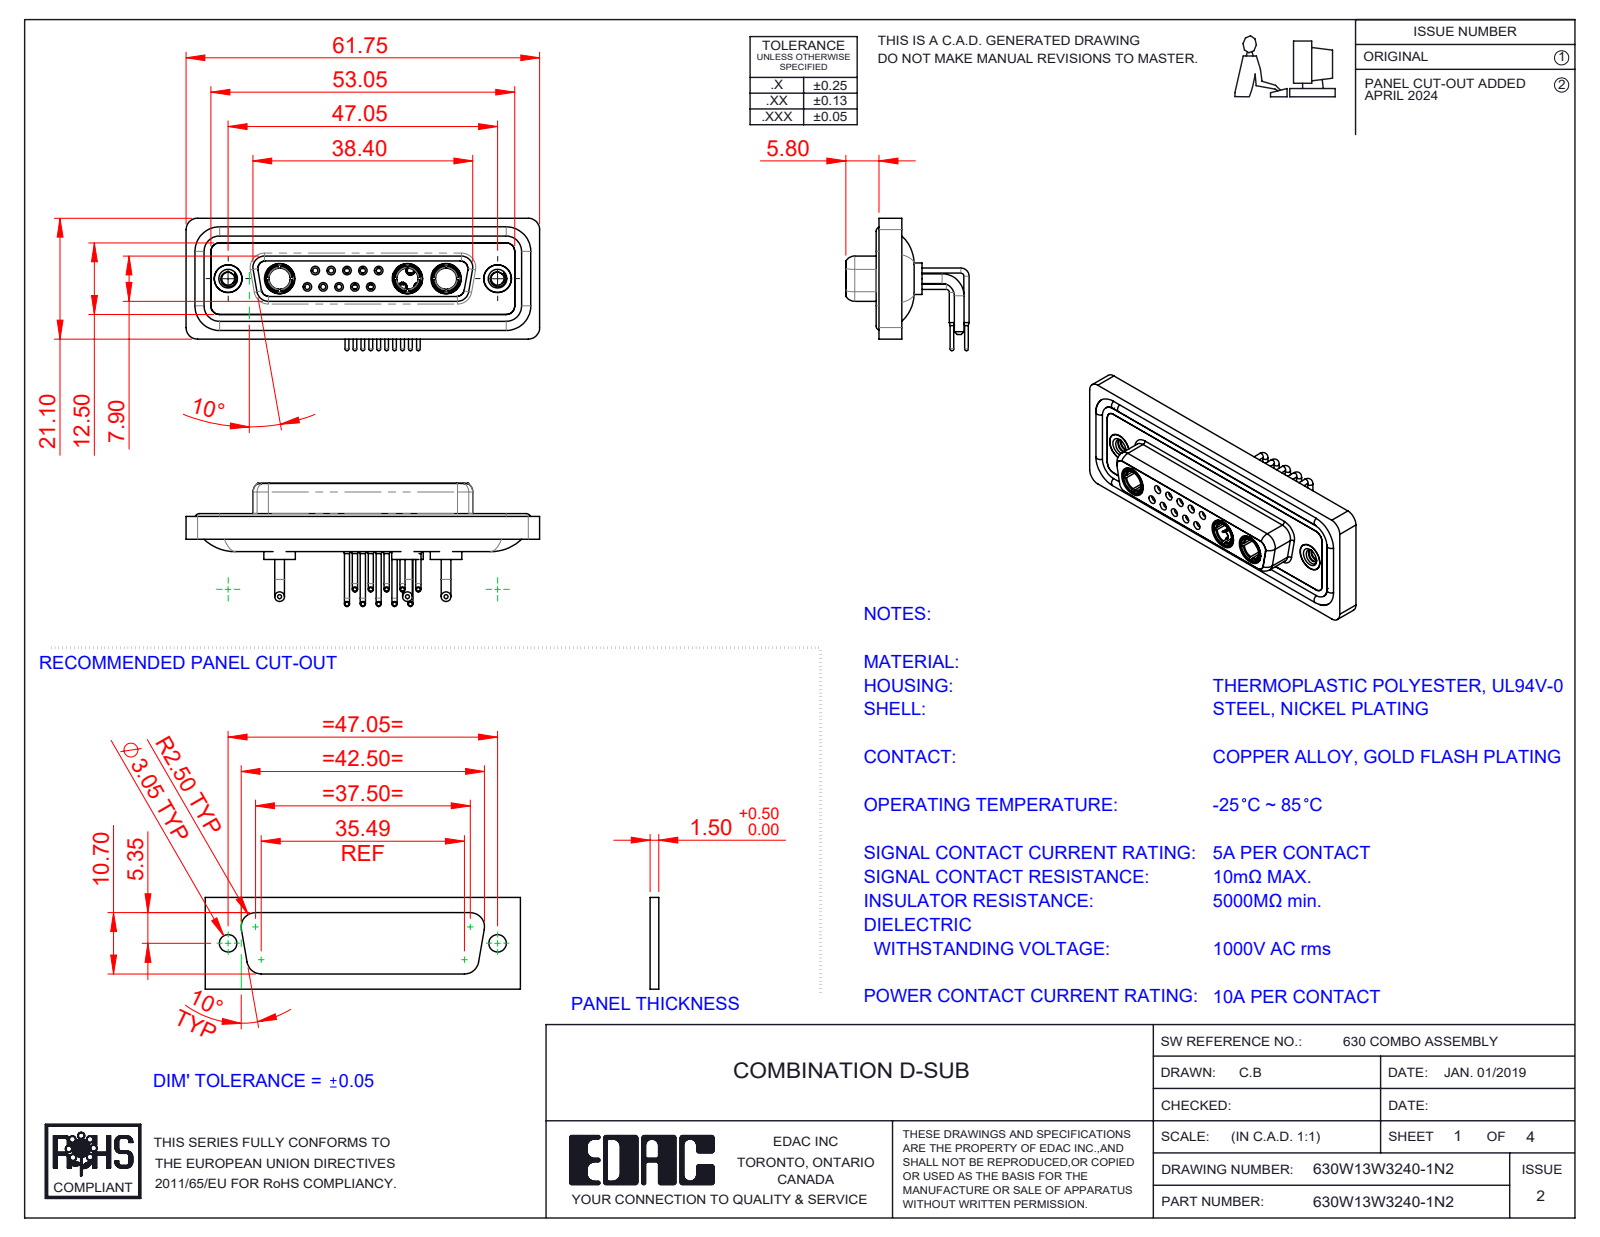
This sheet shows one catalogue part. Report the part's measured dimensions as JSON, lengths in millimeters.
{"part_name": "630Combo Contact Row 2_50 Contacts; Power Socket_10A RA; 630Combo Housing_13W3; 630Combo Shell Rear_25 Contacts (+5 more)", "step_written_by": "SolidWorks 2023 (CONFIG_CONTROL_DESIGN)", "units": "millimeters", "bodies": {"solids": 23, "faces": 1150, "planar": 342, "cylindrical": 493, "other": 315}, "overall_size": [61.75, 23.12, 21.53], "volume_mm3": 8297, "surface_area_mm2": 14144, "round_holes": [[0.9, 10], [1.1, 10], [1.5, 10], [2, 10], [1.6, 5], [1.7, 5], [4.85, 5], [3.7, 3], [5.3, 3], [2.26, 2], [4, 2], [4.05, 2]], "round_bosses_or_shafts": [[0.9, 15], [1.6, 12], [0.65, 10], [1.7, 6], [2, 5], [1.5, 5], [5.5, 3], [5.2, 3]], "partial_cylinders_radius": [[1.5, 18], [2, 18], [1.35, 8], [1.6, 8], [0.25, 4], [0.5, 4], [0.6, 4], [0.65, 4]], "face_to_face_distances": [0.4, 1.8, 4.1, 1.1, 1.6, 1.5, 3.1, 2.5, 3.7, 1.4], "hole_center_spacings": [3.16, 2.77, 5.54, 5.04, 8.31, 5.03, 7.49, 11.08]}
